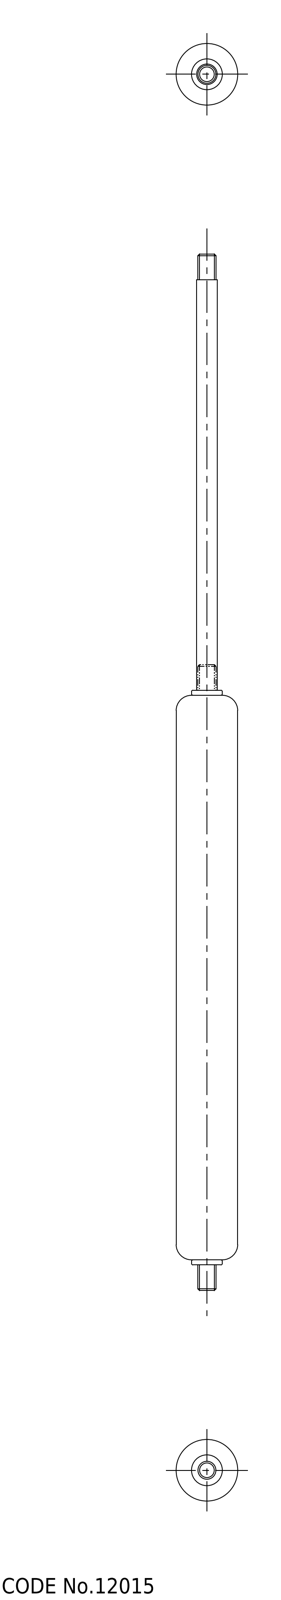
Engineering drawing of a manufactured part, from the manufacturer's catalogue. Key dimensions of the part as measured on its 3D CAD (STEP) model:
Part name (STEP PRODUCT): rod; TM_278_80_50_30469_36
STEP written by: CADfix (AUTOMOTIVE_DESIGN)
Units: millimetres
Bodies: 2 solids, 36 faces (0 planar, 0 cylindrical, 36 other)
Overall size (bounding box): 202 × 12 × 12
Volume: 13 495 mm³ · Surface area: 5 478 mm²
